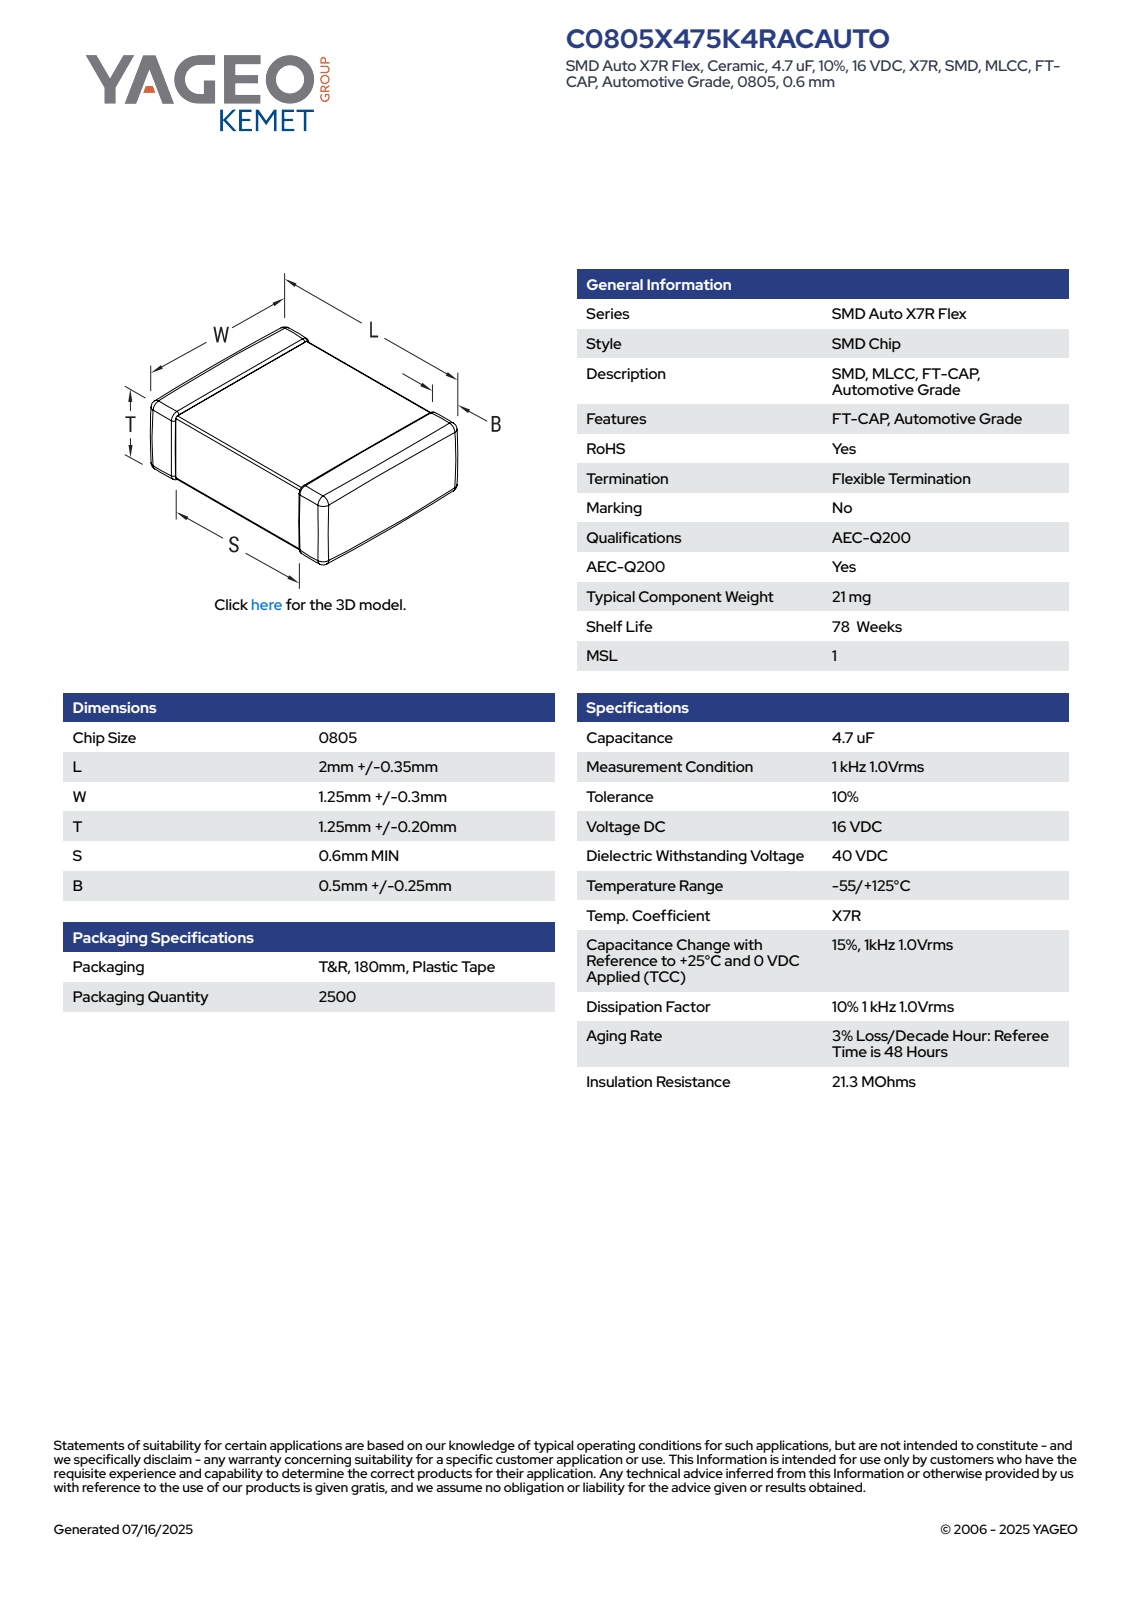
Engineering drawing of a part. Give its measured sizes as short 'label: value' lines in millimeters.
name: CCS_CCSTD_0805_L2.35W1.55T1.45B0.5
written by: SolidWorks 2021 (AUTOMOTIVE_DESIGN)
unit: mm
bodies: 4 solids, 125 faces (71 planar, 38 cylindrical, 16 other)
size: 2.35 × 1.55 × 1.45
volume: 5 mm³; area: 19 mm²
face distances: 1.42, 1.52, 2.35, 1.45, 1.55, 1.39, 1.49, 1.04, 1.31, 1.08
